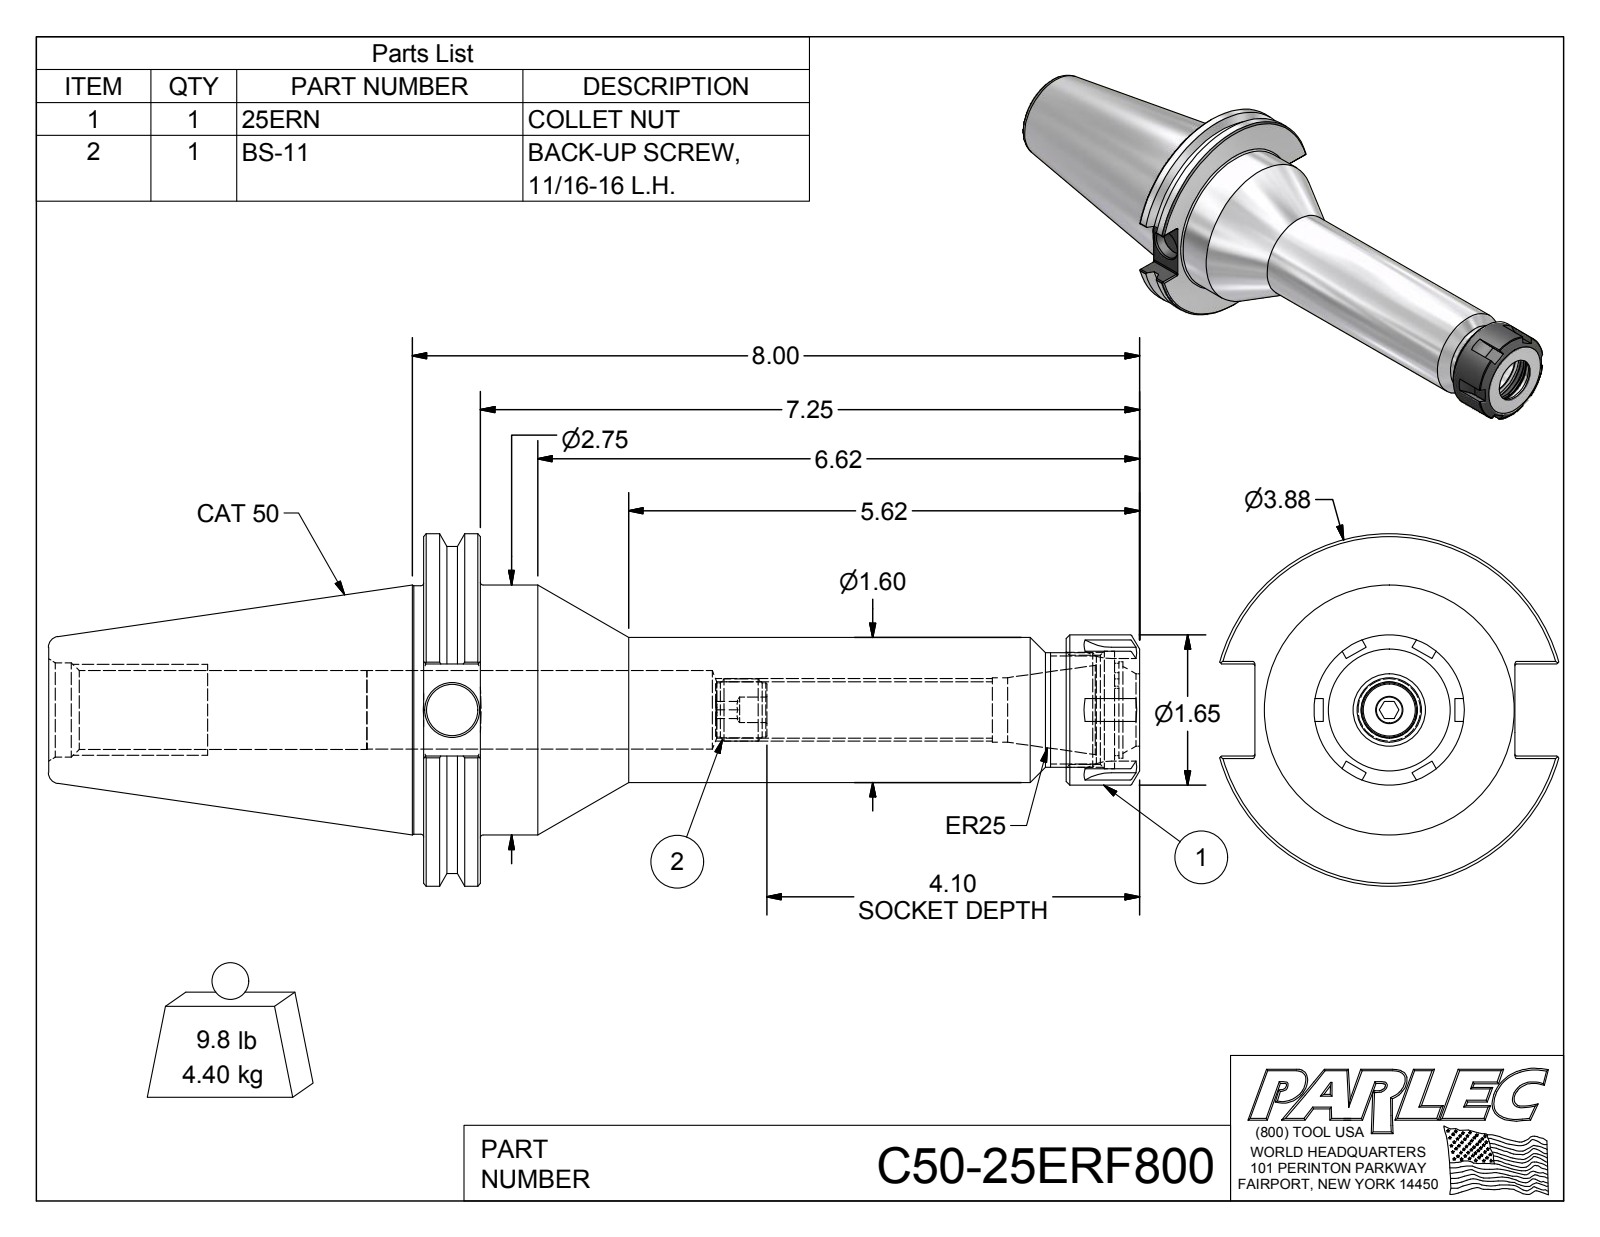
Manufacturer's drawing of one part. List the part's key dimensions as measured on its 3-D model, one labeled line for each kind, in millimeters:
Part name (STEP PRODUCT): C50-25ER8-1; 25ERN; BS-11; C50-25ERF800
STEP written by: Autodesk Inventor 2016 (AUTOMOTIVE_DESIGN)
Units: millimetres
Bodies: 3 solids, 181 faces (71 planar, 50 cylindrical, 60 other)
Overall size (bounding box): 304.8 × 98.42 × 94.71
Volume: 538 106 mm³ · Surface area: 84 311 mm²
Round holes (diameter × count): ⌀7.11 ×1, ⌀14.3 ×1, ⌀15.75 ×1, ⌀18.03 ×1, ⌀20.32 ×1, ⌀21.97 ×1, ⌀26.37 ×1, ⌀30.5 ×1, ⌀32.88 ×1
Round bosses / shafts (diameter × count): ⌀98.42 ×1, ⌀91.29 ×1, ⌀69.85 ×1, ⌀69.34 ×1, ⌀42 ×1, ⌀40.51 ×1, ⌀32 ×1, ⌀17.3 ×1
Partial cylindrical surfaces — rounded edges, fillets, slot ends (radius × count): R0.51 ×24, R12 ×1, R13.06 ×1, R13.43 ×1
Main face-to-face distances: 15.88, 31.88, 16, 200.03, 184.15, 168.15, 179.46, 163.58, 147.58, 20.57
